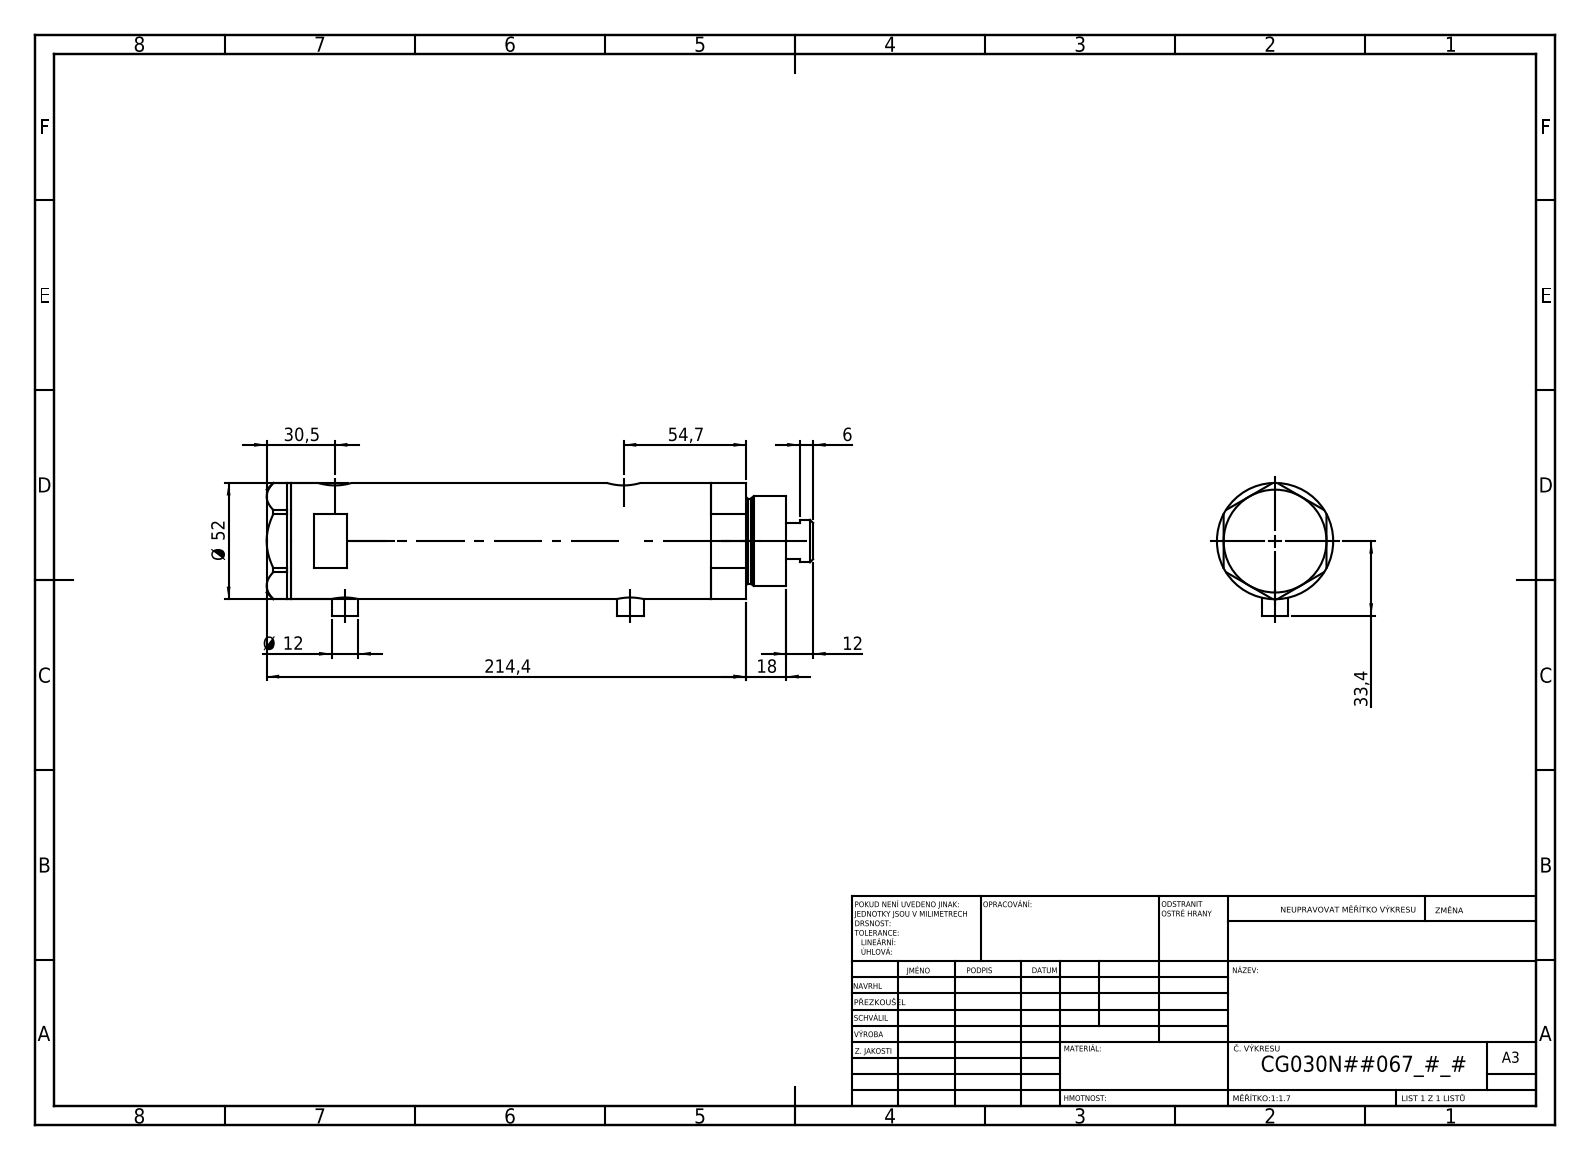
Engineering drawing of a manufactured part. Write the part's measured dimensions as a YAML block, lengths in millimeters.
part_name: "V270CG_BACK; V270CG_MIDDLE; V270CG_VC; V270CG_FRONT"
step_written_by: "SolidWorks 2019 (CONFIG_CONTROL_DESIGN)"
units: millimeters
bodies: {solids: 4, faces: 134, planar: 65, cylindrical: 49, other: 20}
overall_size: [244.4, 59.4, 52]
volume: 447813
surface_area: 97084
round_holes:
  - {diameter: 9.73, count: 2}
  - {diameter: 12.5, count: 2}
  - {diameter: 15, count: 2}
  - {diameter: 6.5, count: 1}
  - {diameter: 20, count: 1}
  - {diameter: 21.5, count: 1}
  - {diameter: 30, count: 1}
  - {diameter: 33, count: 1}
  - {diameter: 44, count: 1}
round_bosses_or_shafts:
  - {diameter: 12, count: 2}
  - {diameter: 52, count: 1}
  - {diameter: 40, count: 1}
  - {diameter: 38, count: 1}
  - {diameter: 19, count: 1}
face_to_face_distances: [151.5, 23.8, 127.7, 11, 34.8, 162.5, 46, 198.9, 187.9, 164.1]
hole_center_spacings: [2.9, 4.5, 124.7, 127.6, 129.2, 132.1]
